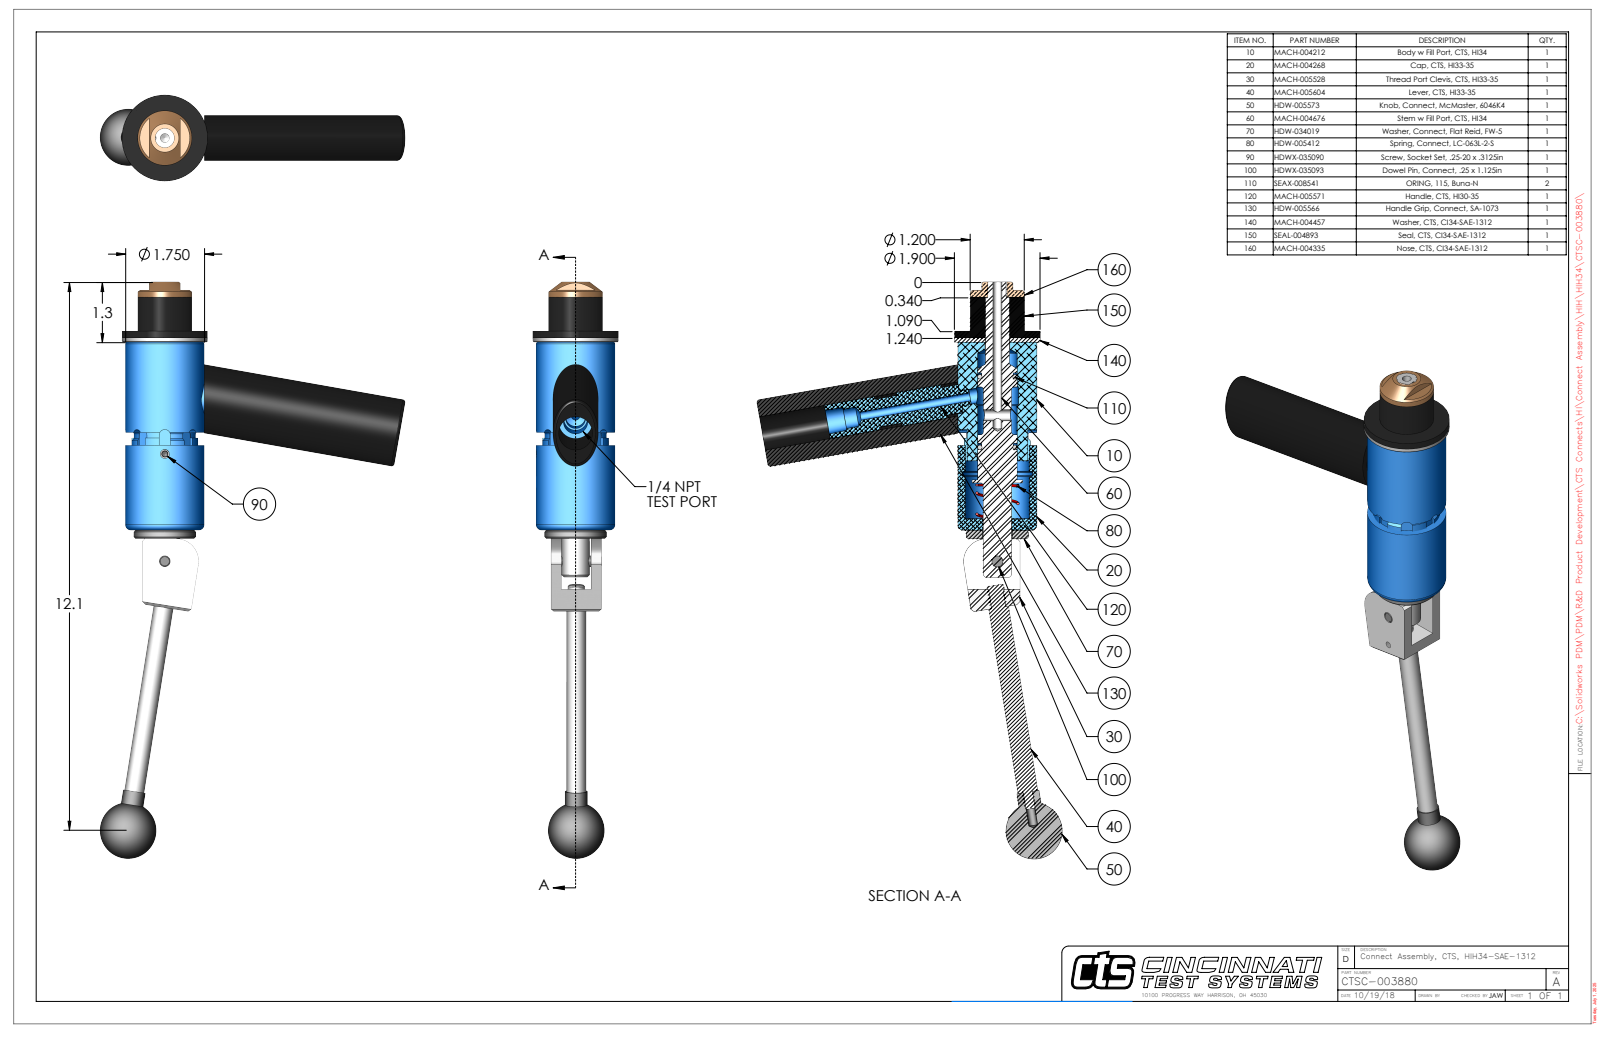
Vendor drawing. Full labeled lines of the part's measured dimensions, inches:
Part name (STEP PRODUCT): CTSC-003880
STEP written by: SolidWorks 2023 (AUTOMOTIVE_DESIGN)
Units: inches
Bodies: 10 solids, 323 faces (117 planar, 138 cylindrical, 68 other)
Overall size (bounding box): 12.773 × 6.763 × 1.9
Volume: 19.08 in³ · Surface area: 123 in²
Round holes (diameter × count): ⌀0.201 ×2, ⌀0.15 ×1, ⌀0.187 ×1, ⌀0.204 ×1, ⌀0.249 ×1, ⌀0.25 ×1, ⌀0.251 ×1, ⌀0.313 ×1, ⌀0.422 ×1, ⌀0.438 ×1, ⌀0.53 ×1, ⌀0.541 ×1
Round bosses / shafts (diameter × count): ⌀0.5 ×2, ⌀0.44 ×2, ⌀0.25 ×2, ⌀1.9 ×1, ⌀1.75 ×1, ⌀1.38 ×1, ⌀1.2 ×1, ⌀0.75 ×1
Partial cylindrical surfaces — rounded edges, fillets, slot ends (radius × count): R0.125 ×4, R0.029 ×2, R0.166 ×1, R0.168 ×1, R0.33 ×1, R0.5 ×1, R0.695 ×1, R0.709 ×1
Main face-to-face distances: 0.094, 4.258, 4.164, 0.9, 0.994, 5.158, 0.75, 0.15, 0.244, 4.408
Hole centre spacings: 0.74, 2.376, 3.116
